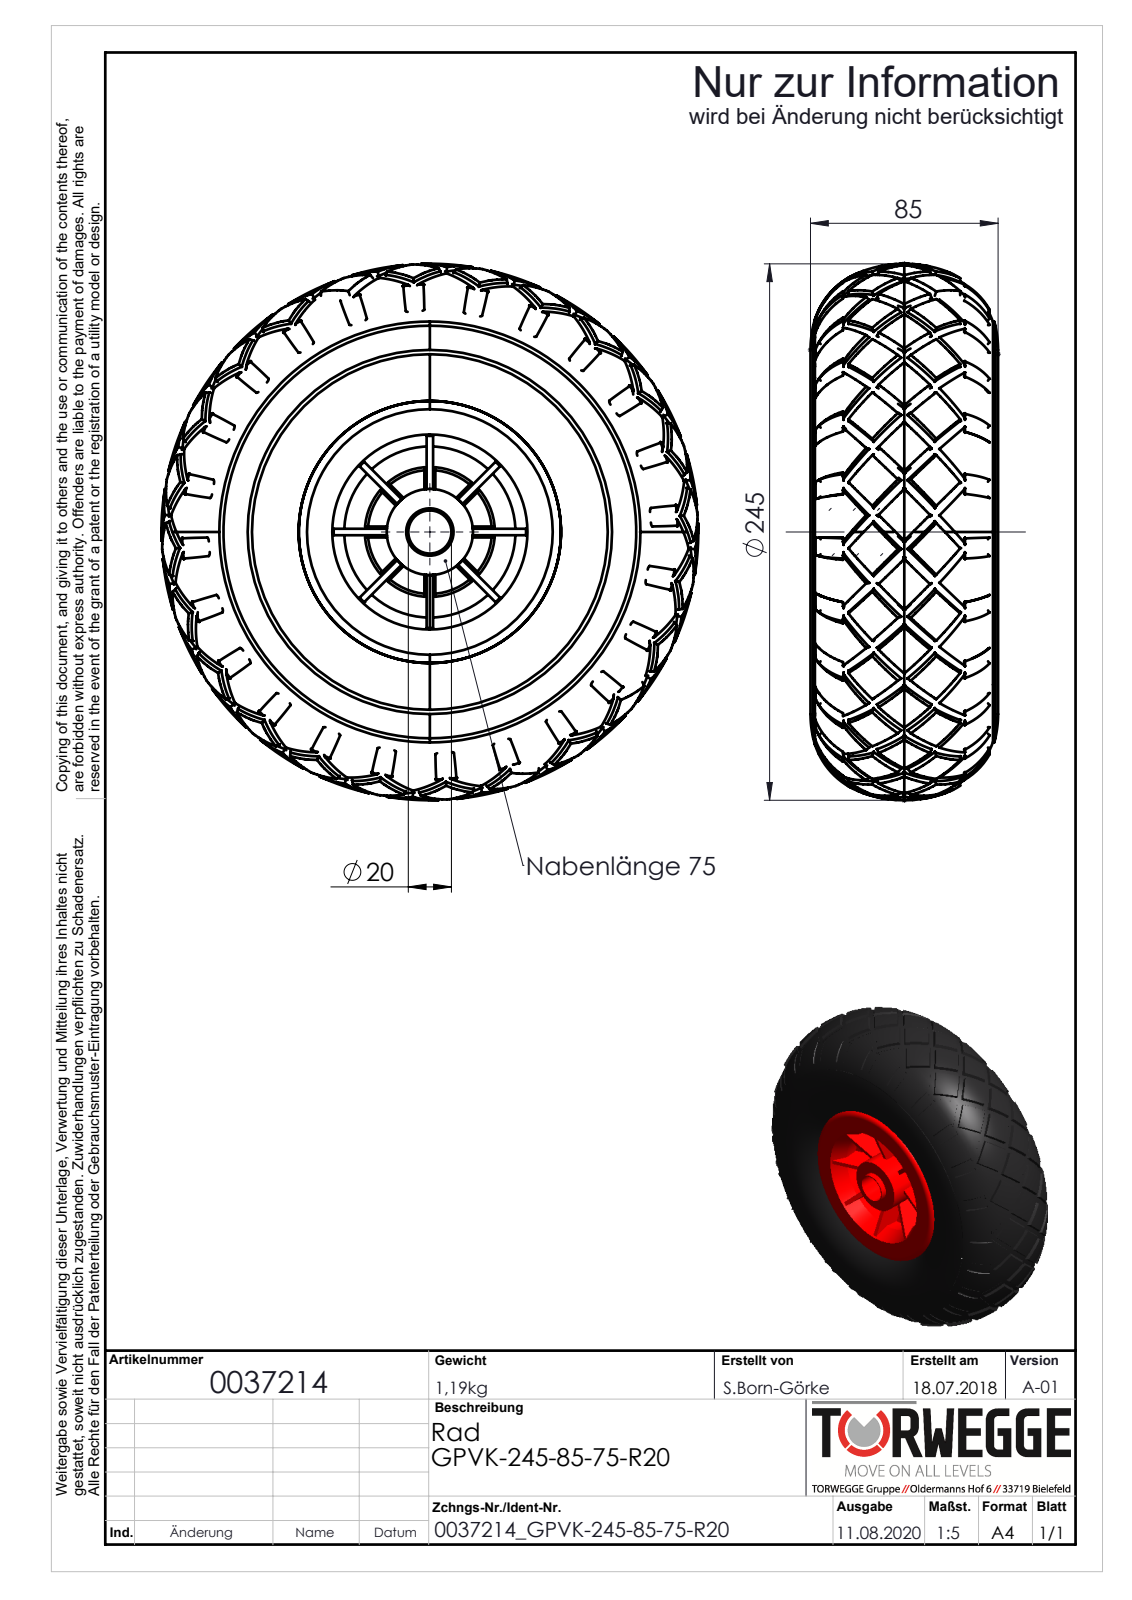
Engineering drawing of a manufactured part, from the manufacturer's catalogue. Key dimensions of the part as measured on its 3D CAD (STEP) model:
Part name (STEP PRODUCT): 0037214
STEP written by: SolidWorks 2018 (AUTOMOTIVE_DESIGN)
Units: millimetres
Bodies: 0 solids, 1419 faces (140 planar, 10 cylindrical, 1269 other)
Overall size (bounding box): 249 × 249 × 87
Round holes (diameter × count): ⌀20 ×1, ⌀22 ×1
Round bosses / shafts (diameter × count): ⌀40 ×1, ⌀35 ×1
Main face-to-face distances: 74.66, 33.38, 41.28, 6.17, 39.55, 47.45, 80.83, 4.74, 4.76, 4.72
